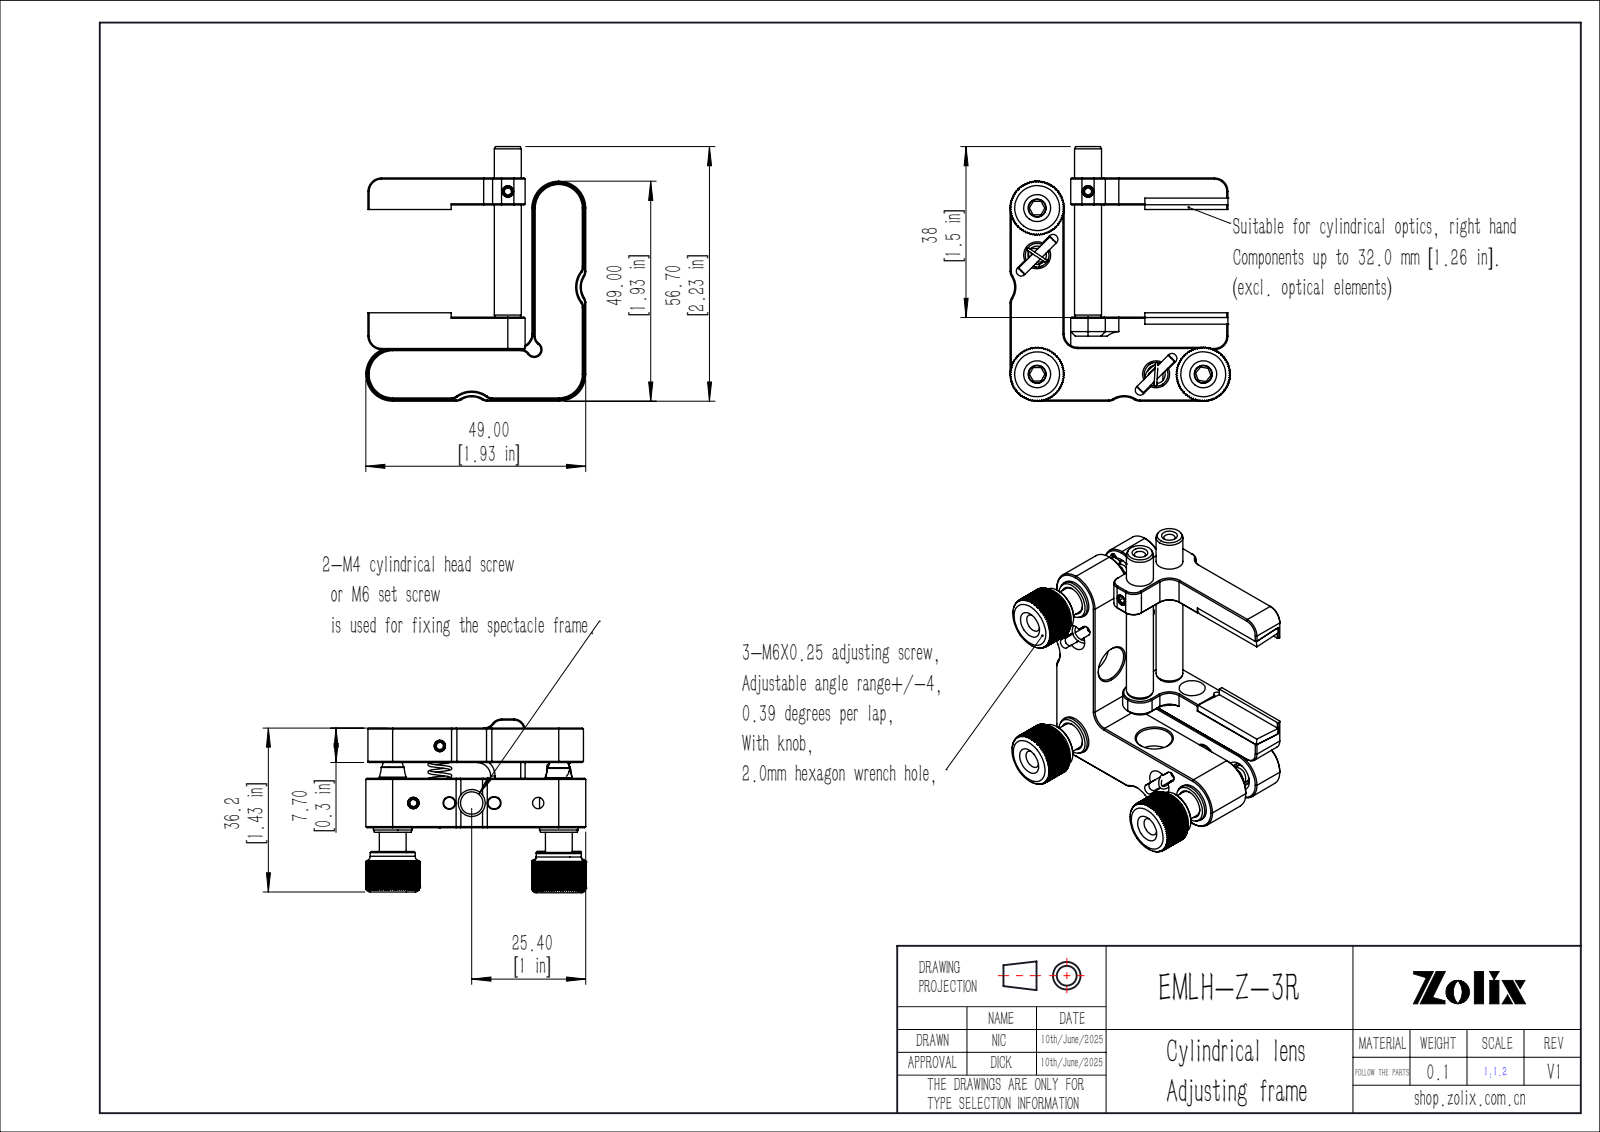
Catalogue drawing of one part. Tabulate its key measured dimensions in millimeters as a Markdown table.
| quantity | value |
| --- | --- |
| part name | EMLH-Z-3R |
| STEP written by | SolidWorks 2020 (CONFIG_CONTROL_DESIGN) |
| units | millimeters |
| bodies | 0 solids, 1238 faces (646 planar, 366 cylindrical, 226 other) |
| overall size | 56.7 × 49 × 38.7 |
| round holes (diameter × count) | 2.5 × 6, 6 × 4, 4 × 3, 9.8 × 3, 5 × 2, 8 × 2, 4.5 × 1, 5.2 × 1, 5.8 × 1 |
| round bosses / shafts (diameter × count) | 6 × 5, 10 × 3, 8.6 × 3, 2 × 2, 1.5 × 2, 9.5 × 1, 3 × 1 |
| partial cylindrical surfaces (radius × count) | 2 × 10, 2.5 × 5, 5.5 × 5, 1.1 × 4, 1.25 × 4, 3 × 4, 0.8 × 3, 6 × 3 |
| main face-to-face distances | 11, 7.7, 11.5, 0.5, 3.5, 11.2, 14.5, 22.2, 12, 8.2 |
| hole center spacings | 5, 10.5, 26.5, 37, 45.51, 7.15, 7.63, 8.8 |
